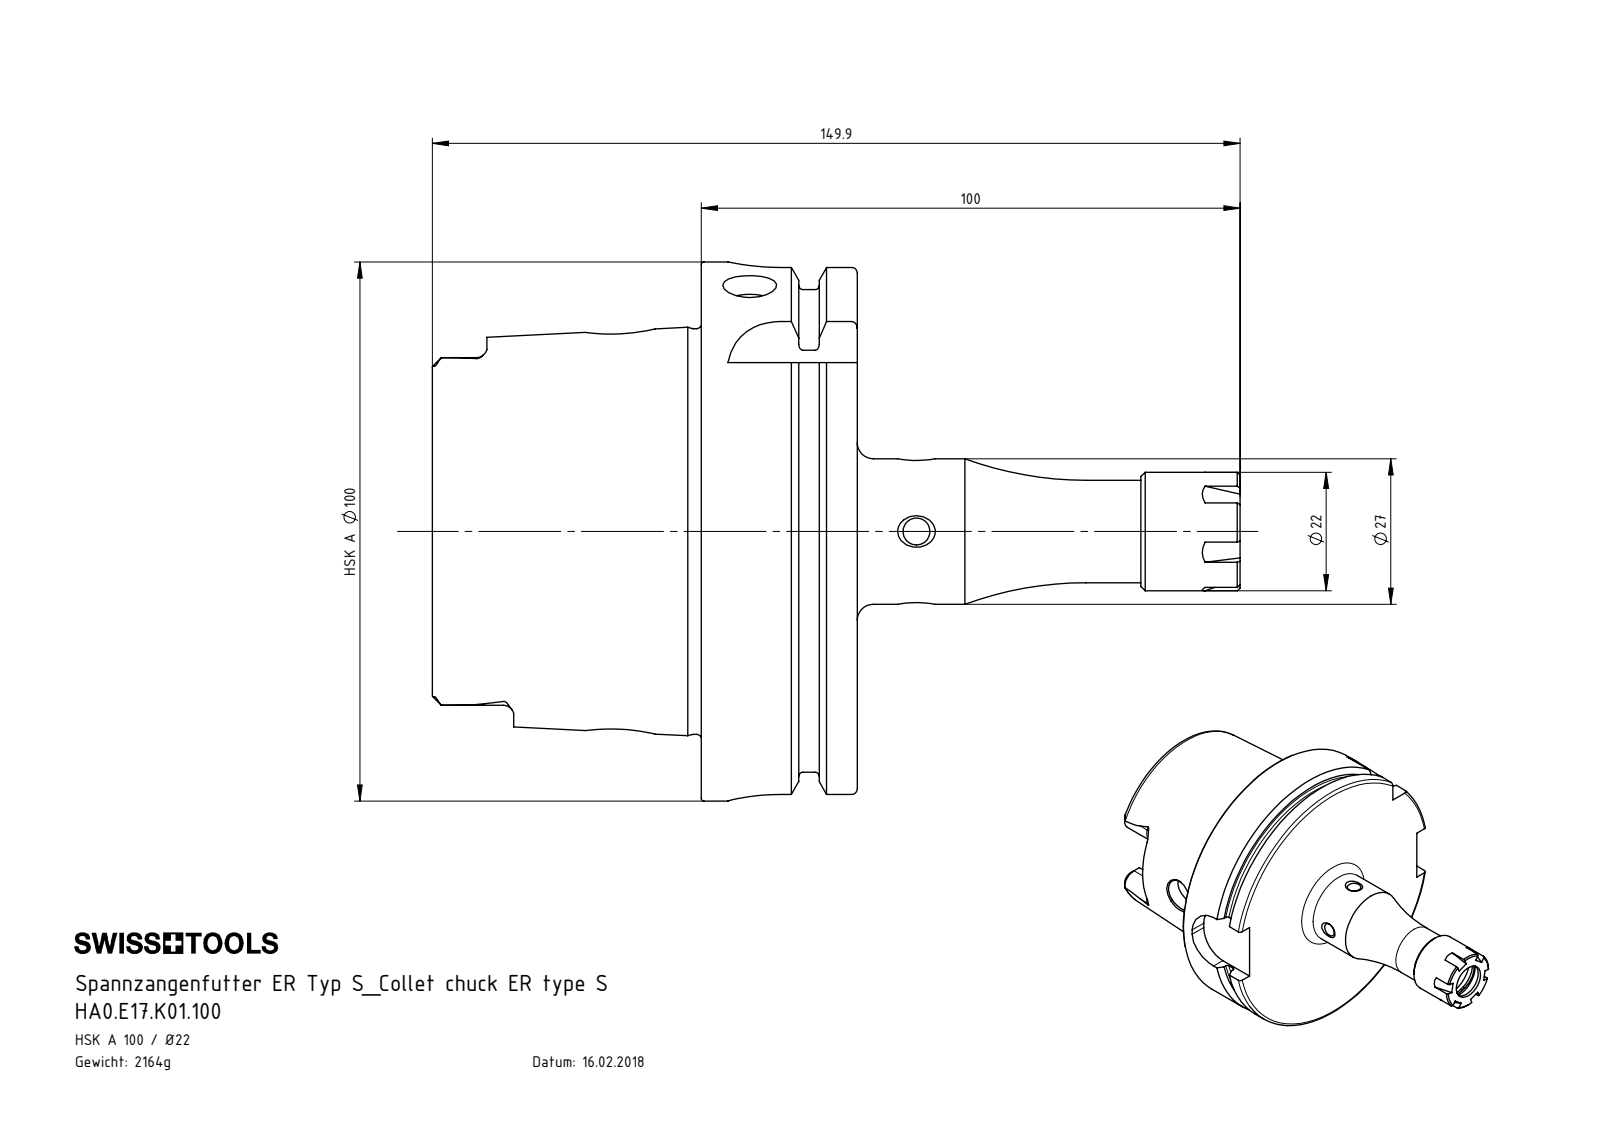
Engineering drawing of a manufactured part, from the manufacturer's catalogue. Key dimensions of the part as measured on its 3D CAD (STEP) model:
Part name (STEP PRODUCT): ERU-AN2.K01.016_A; HA0.E17.K01.100; HA0-E17.K01.100_C_Fertigbearbeitung; E17-ER1.001.018
STEP written by: SolidWorks 2017 (CONFIG_CONTROL_DESIGN)
Units: millimetres
Bodies: 3 solids, 295 faces (99 planar, 81 cylindrical, 115 other)
Overall size (bounding box): 149.9 × 100 × 100
Volume: 275 603 mm³ · Surface area: 58 922 mm²
Round holes (diameter × count): ⌀5 ×3, ⌀10 ×3, ⌀3 ×1, ⌀6.8 ×1, ⌀10.5 ×1, ⌀12 ×1, ⌀12.7 ×1, ⌀18 ×1, ⌀20 ×1, ⌀22.5 ×1, ⌀26 ×1, ⌀53 ×1
Round bosses / shafts (diameter × count): ⌀100 ×1, ⌀91.95 ×1, ⌀75.26 ×1, ⌀27 ×1, ⌀22 ×1, ⌀19 ×1, ⌀6 ×1
Partial cylindrical surfaces — rounded edges, fillets, slot ends (radius × count): R1.9 ×6, R4.88 ×4, R10 ×4, R7.7 ×2
Main face-to-face distances: 28.95, 12.45, 16.5, 49.9, 62.35, 78.85, 78.2, 28.3, 15.85, 0.65
Hole centre spacings: 32.95, 54.95
